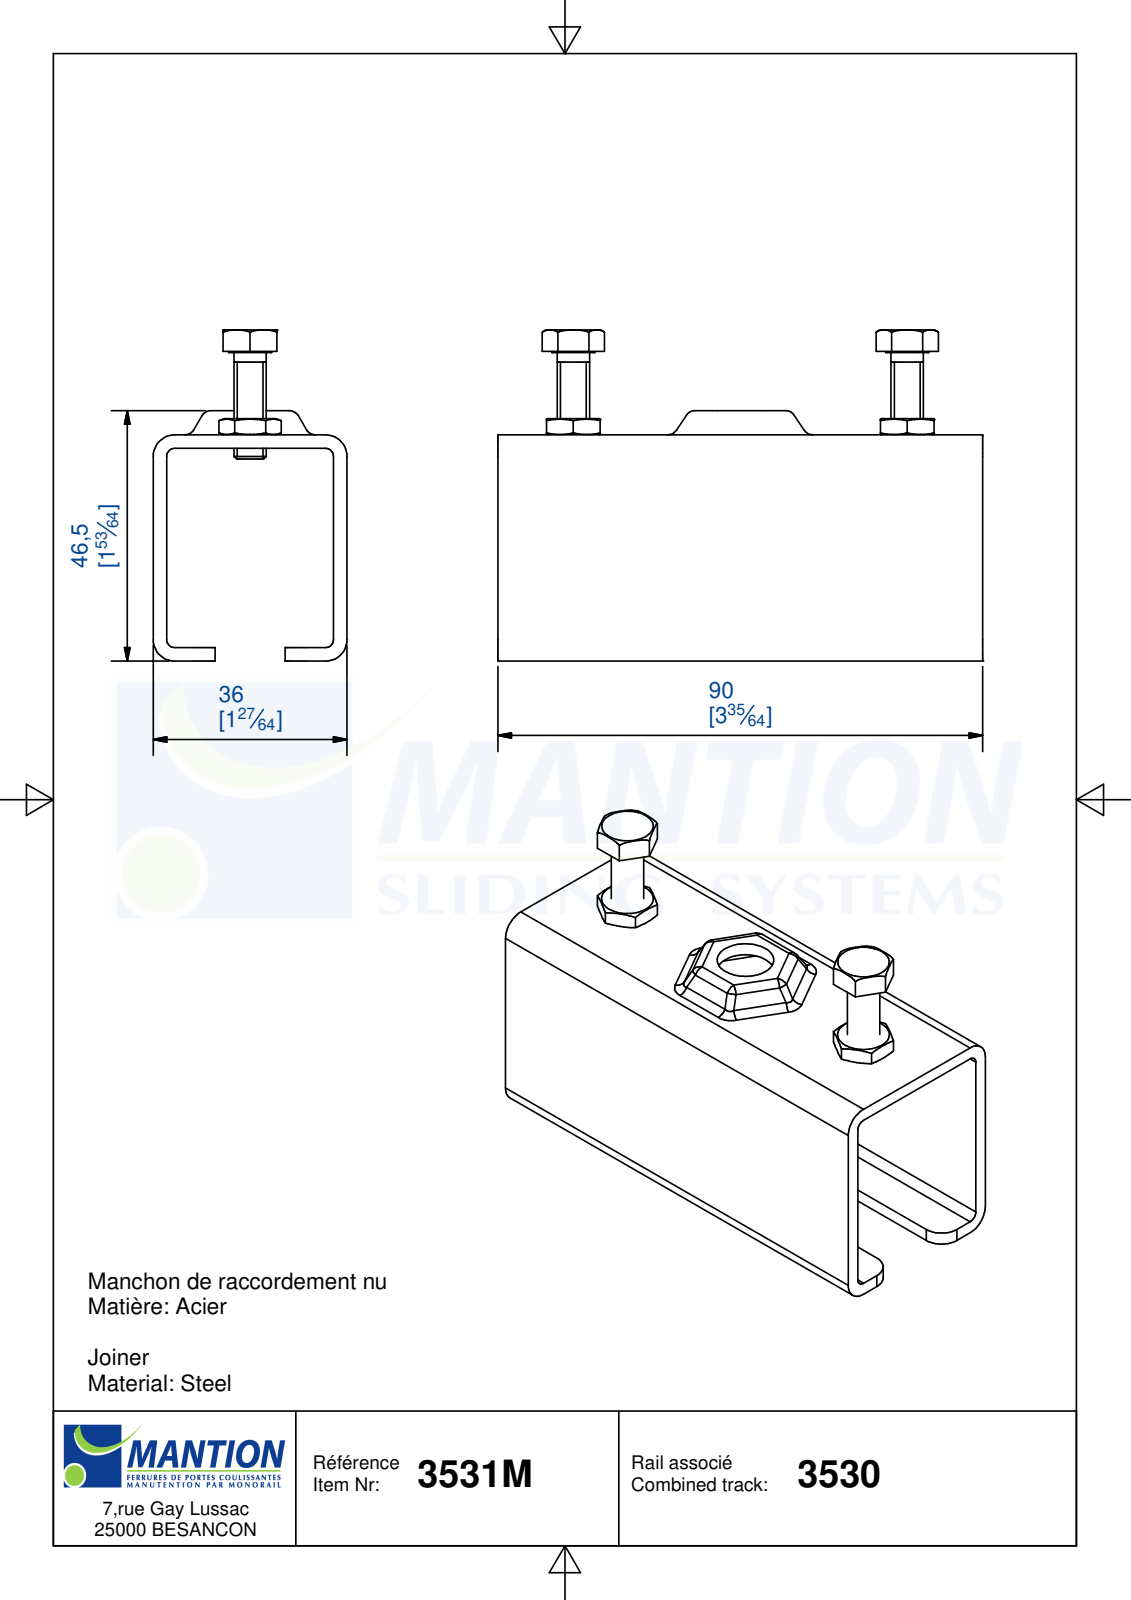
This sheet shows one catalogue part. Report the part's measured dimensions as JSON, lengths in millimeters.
{"part_name": "3531M; 15301; VIS TH M6x20; vis TH M6x20 helicoidal (+1 more)", "step_written_by": "Autodesk Inventor 2011 (AUTOMOTIVE_DESIGN)", "units": "millimeters", "bodies": {"solids": 5, "faces": 113, "planar": 44, "cylindrical": 49, "other": 20}, "overall_size": [90, 61.5, 36], "volume_mm3": 30587, "surface_area_mm2": 27059, "round_holes": [[4.92, 2], [5, 2], [10.5, 1]], "partial_cylinders_radius": [[2, 18], [3, 12], [4, 8], [1.5, 4]], "face_to_face_distances": [2.5, 33.5, 36, 31, 39.5, 37, 42, 22, 9, 11.5], "hole_center_spacings": [31, 62]}
